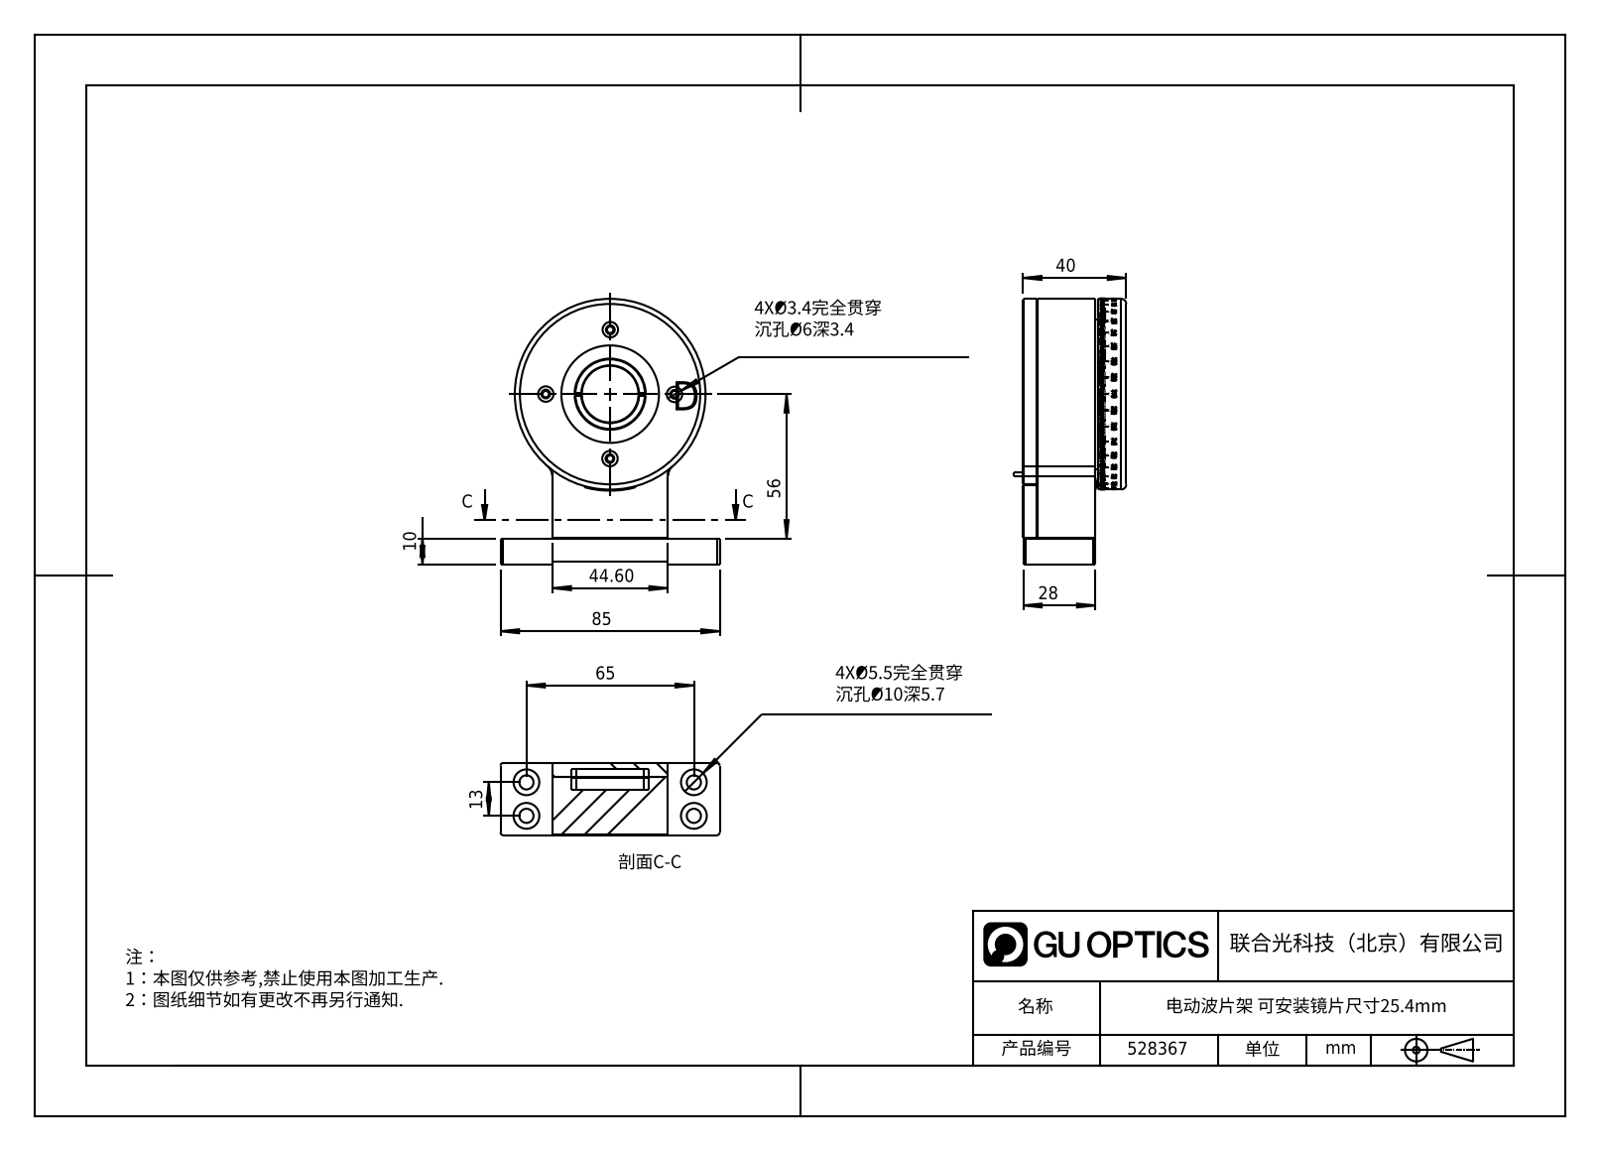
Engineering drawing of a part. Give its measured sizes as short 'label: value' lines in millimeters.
name: 528367
written by: SolidWorks 2020 (CONFIG_CONTROL_DESIGN)
unit: mm
bodies: 0 solids, 455 faces (262 planar, 149 cylindrical, 44 other)
size: 103 × 85 × 43.75
holes: 16× ⌀1.25, 16× ⌀1.8, 12× ⌀3.5, 8× ⌀3.3, 5× ⌀2.5, 4× ⌀3.4, 4× ⌀4.5, 4× ⌀5.5, 4× ⌀6, 4× ⌀8, 4× ⌀10, 2× ⌀2.05
bosses: 1× ⌀74, 1× ⌀66, 1× ⌀65.5, 1× ⌀28, 1× ⌀3
rounds: 16× R0.5, 8× R2, 4× R1, 2× R0.1, 2× R5, 1× R18, 1× R37.25
face distances: 28, 34.5, 5.5, 40, 1, 0.5, 29.5, 23.5, 1.5, 10.5
hole spacings: 35, 31, 33.18, 57.19, 25, 35.36, 50, 4
